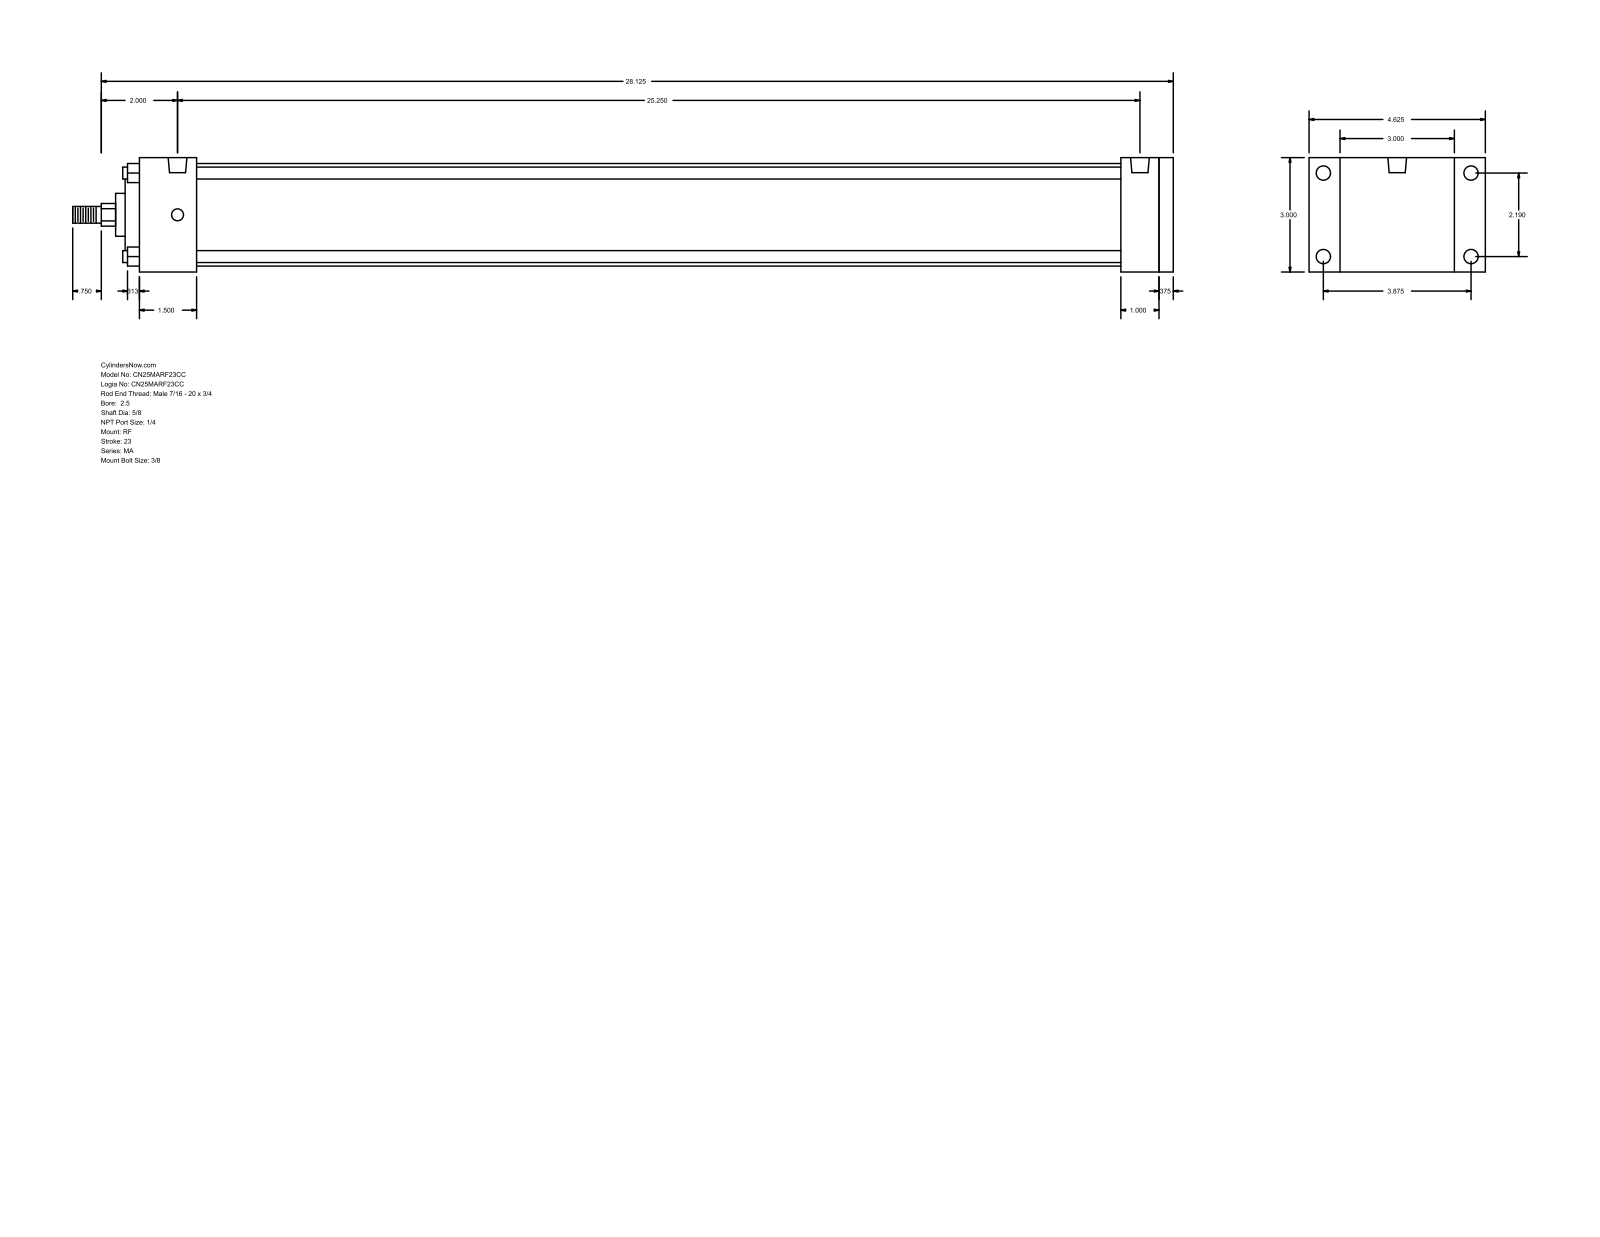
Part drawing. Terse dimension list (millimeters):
name: MA_RF__0250_0.625
written by: GSSL Pune (CONFIG_CONTROL_DESIGN)
unit: mm
bodies: 0 solids, 94 faces (65 planar, 29 cylindrical, 0 other)
size: 733.42 × 117.47 × 76.2
holes: 4× ⌀7.94, 4× ⌀9.53, 2× ⌀12.49
bosses: 4× ⌀7.94, 1× ⌀68.33, 1× ⌀50.8, 1× ⌀28.57, 1× ⌀15.88, 1× ⌀11.11
rounds: 1× R7.54
face distances: 76.2, 688.98, 9.53, 679.45, 25.4, 34.93, 38.1, 654.05, 615.95, 641.35
hole spacings: 55.62, 98.42, 113.05, 641.35
